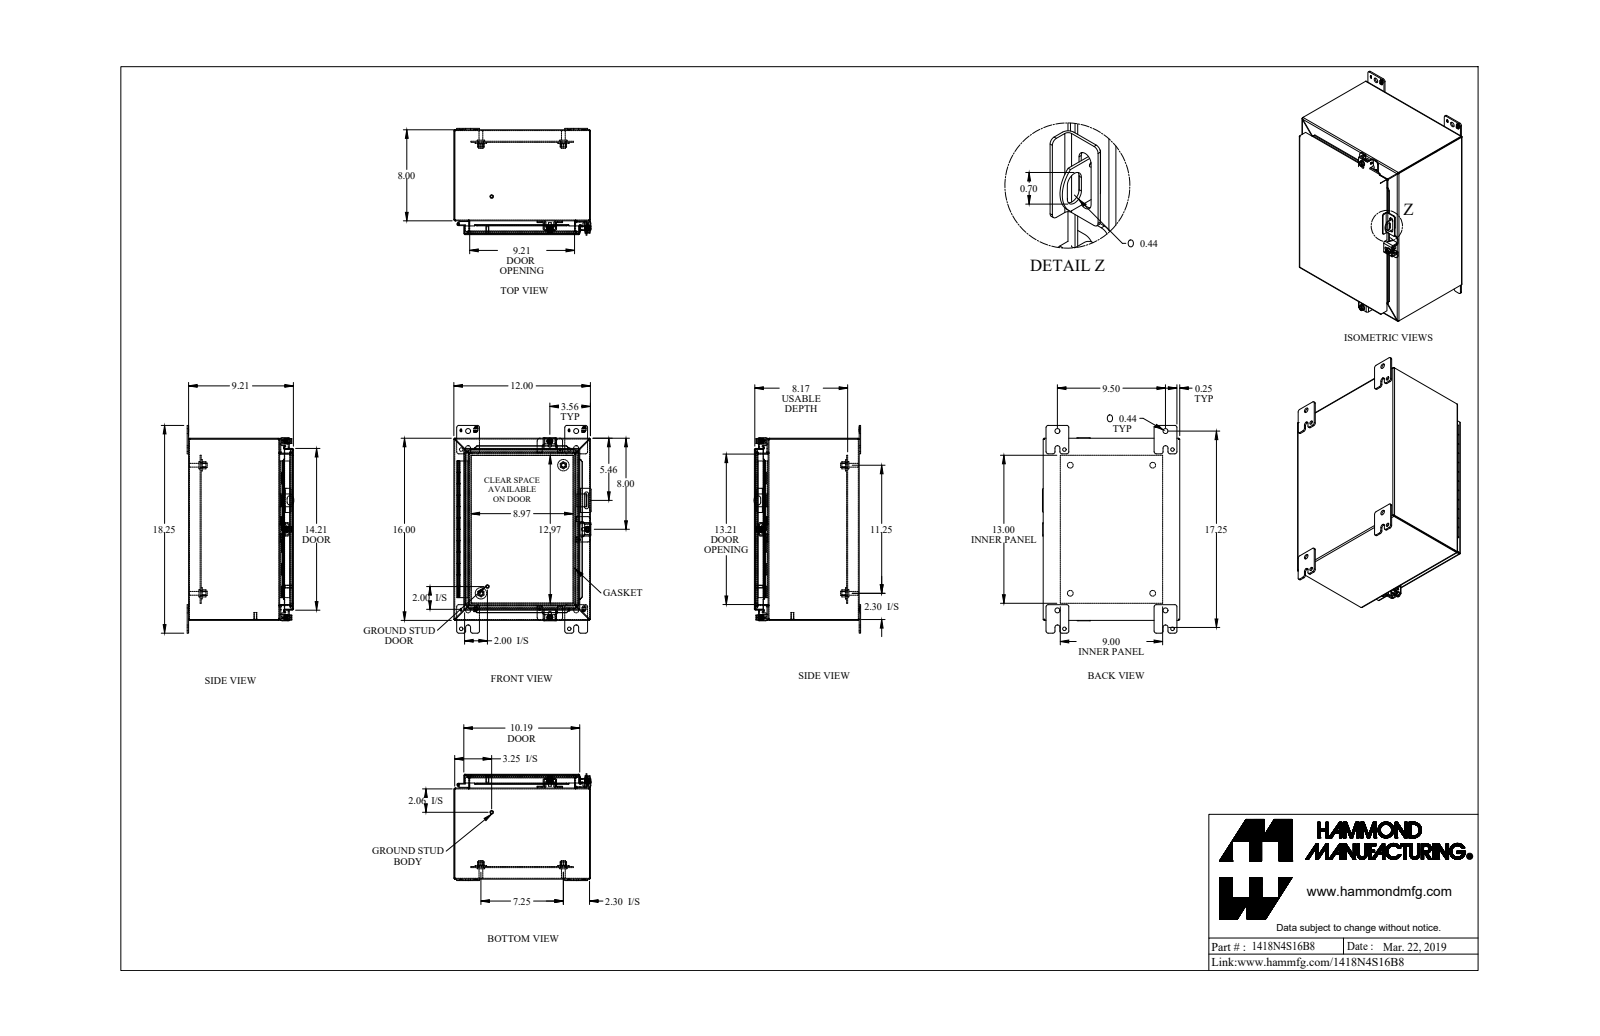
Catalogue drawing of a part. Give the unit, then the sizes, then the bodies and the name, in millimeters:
Units: millimetres
Overall size (bounding box): 463.6 × 306.4 × 238.1
Round holes (diameter × count): ⌀8 ×4, ⌀11.1 ×4, ⌀12.7 ×4, ⌀5.4 ×3, ⌀6.7 ×3, ⌀9.5 ×3, ⌀7.8 ×2, ⌀11.3 ×2, ⌀2.8 ×1, ⌀3.2 ×1
Round bosses / shafts (diameter × count): ⌀16.5 ×4, ⌀9.5 ×4, ⌀8.4 ×4, ⌀12.7 ×3, ⌀9.9 ×3, ⌀6.2 ×3, ⌀25.4 ×2, ⌀8 ×2
Partial cylindrical surfaces — rounded edges, fillets, slot ends (radius × count): R4.8 ×26, R0.9 ×24, R2.7 ×24, R6.4 ×16, R1.2 ×15, R3.6 ×15, R3.2 ×10, R1.1 ×8
Main face-to-face distances: 1.8, 303, 404.6, 230.3, 232.1, 1.8, 232.1, 23.8, 233.9, 25.6
Hole centre spacings: 44.1, 241.3, 400.1, 467.2, 61.8, 184.2, 216.1, 285.8
Volume: 1 459 000 mm³ · Surface area: 1 536 000 mm²
Bodies: 35 solids, 1182 faces (654 planar, 400 cylindrical, 128 other)
Part name (STEP PRODUCT): 1418N4S16B8_Default
STEP written by: SolidWorks 2019 (CONFIG_CONTROL_DESIGN)
